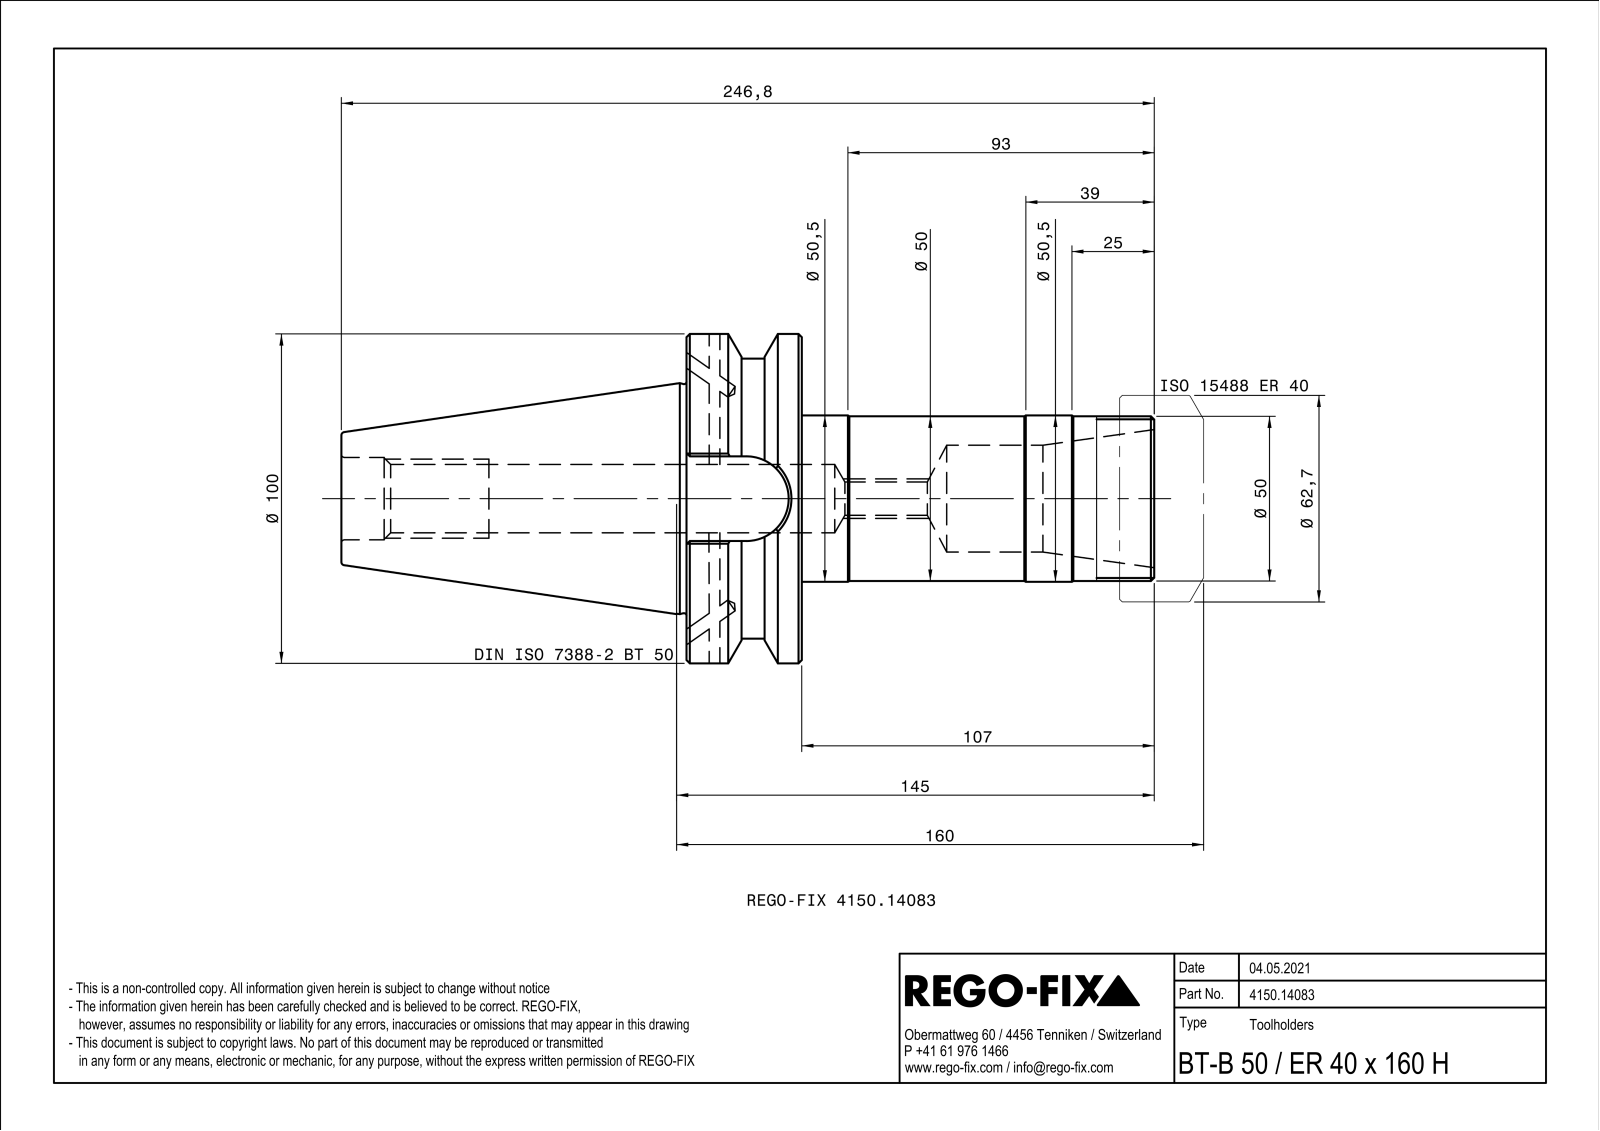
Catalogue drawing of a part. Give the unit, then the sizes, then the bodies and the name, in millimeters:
Units: millimetres
Overall size (bounding box): 246.8 × 100 × 100
Round holes (diameter × count): ⌀3.24 ×2, ⌀3.9 ×2, ⌀10.11 ×1, ⌀20.75 ×1, ⌀25 ×1, ⌀30.5 ×1
Round bosses / shafts (diameter × count): ⌀100 ×1, ⌀85 ×1, ⌀50.5 ×1, ⌀50 ×1
Partial cylindrical surfaces — rounded edges, fillets, slot ends (radius × count): R0.5 ×4, R12.85 ×1
Main face-to-face distances: 35, 70.7, 139.8, 104.8, 107, 142, 246.8, 25.7, 118.3, 11.3
Volume: 591 073 mm³ · Surface area: 79 360 mm²
Bodies: 1 solid, 110 faces (28 planar, 34 cylindrical, 48 other)
Part name (STEP PRODUCT): NOCUT
STEP written by: SIEMENS PLM Software Solid Edge ST10 (AUTOMOTIVE_DESIGN)
